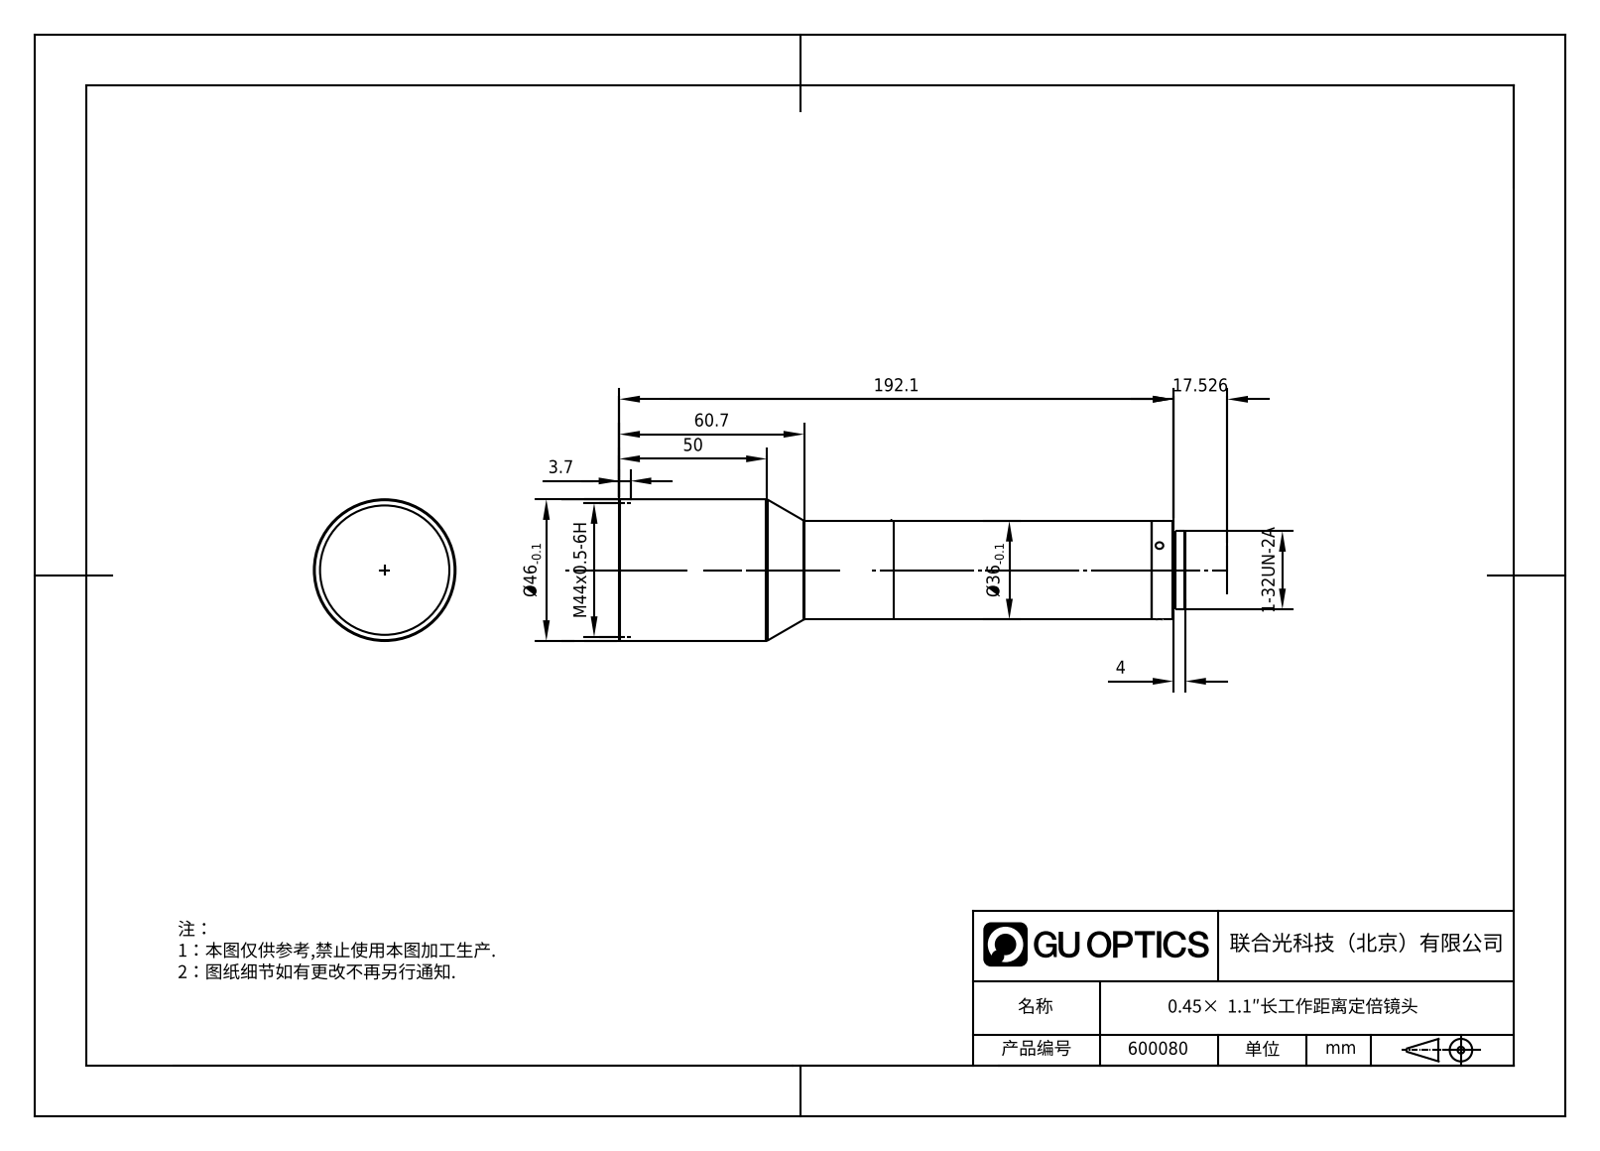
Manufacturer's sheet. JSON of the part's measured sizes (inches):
{"part_name": "600080", "step_written_by": "SolidWorks 2020 (CONFIG_CONTROL_DESIGN)", "units": "inches", "bodies": {"solids": 1, "faces": 25, "planar": 5, "cylindrical": 12, "other": 8}, "overall_size": [7.72, 1.811, 1.811], "volume_in3": 13.85, "surface_area_in2": 43.4, "round_holes": [[0.098, 3], [1.654, 1]], "round_bosses_or_shafts": [[1.811, 1], [1.417, 1], [1, 1], [0.969, 1]], "partial_cylinders_radius": [[0.673, 1]], "face_to_face_distances": [0.157, 7.72, 7.562, 0.551, 0.394, 7.169, 0.126, 0.031, 0.425, 7.594]}
